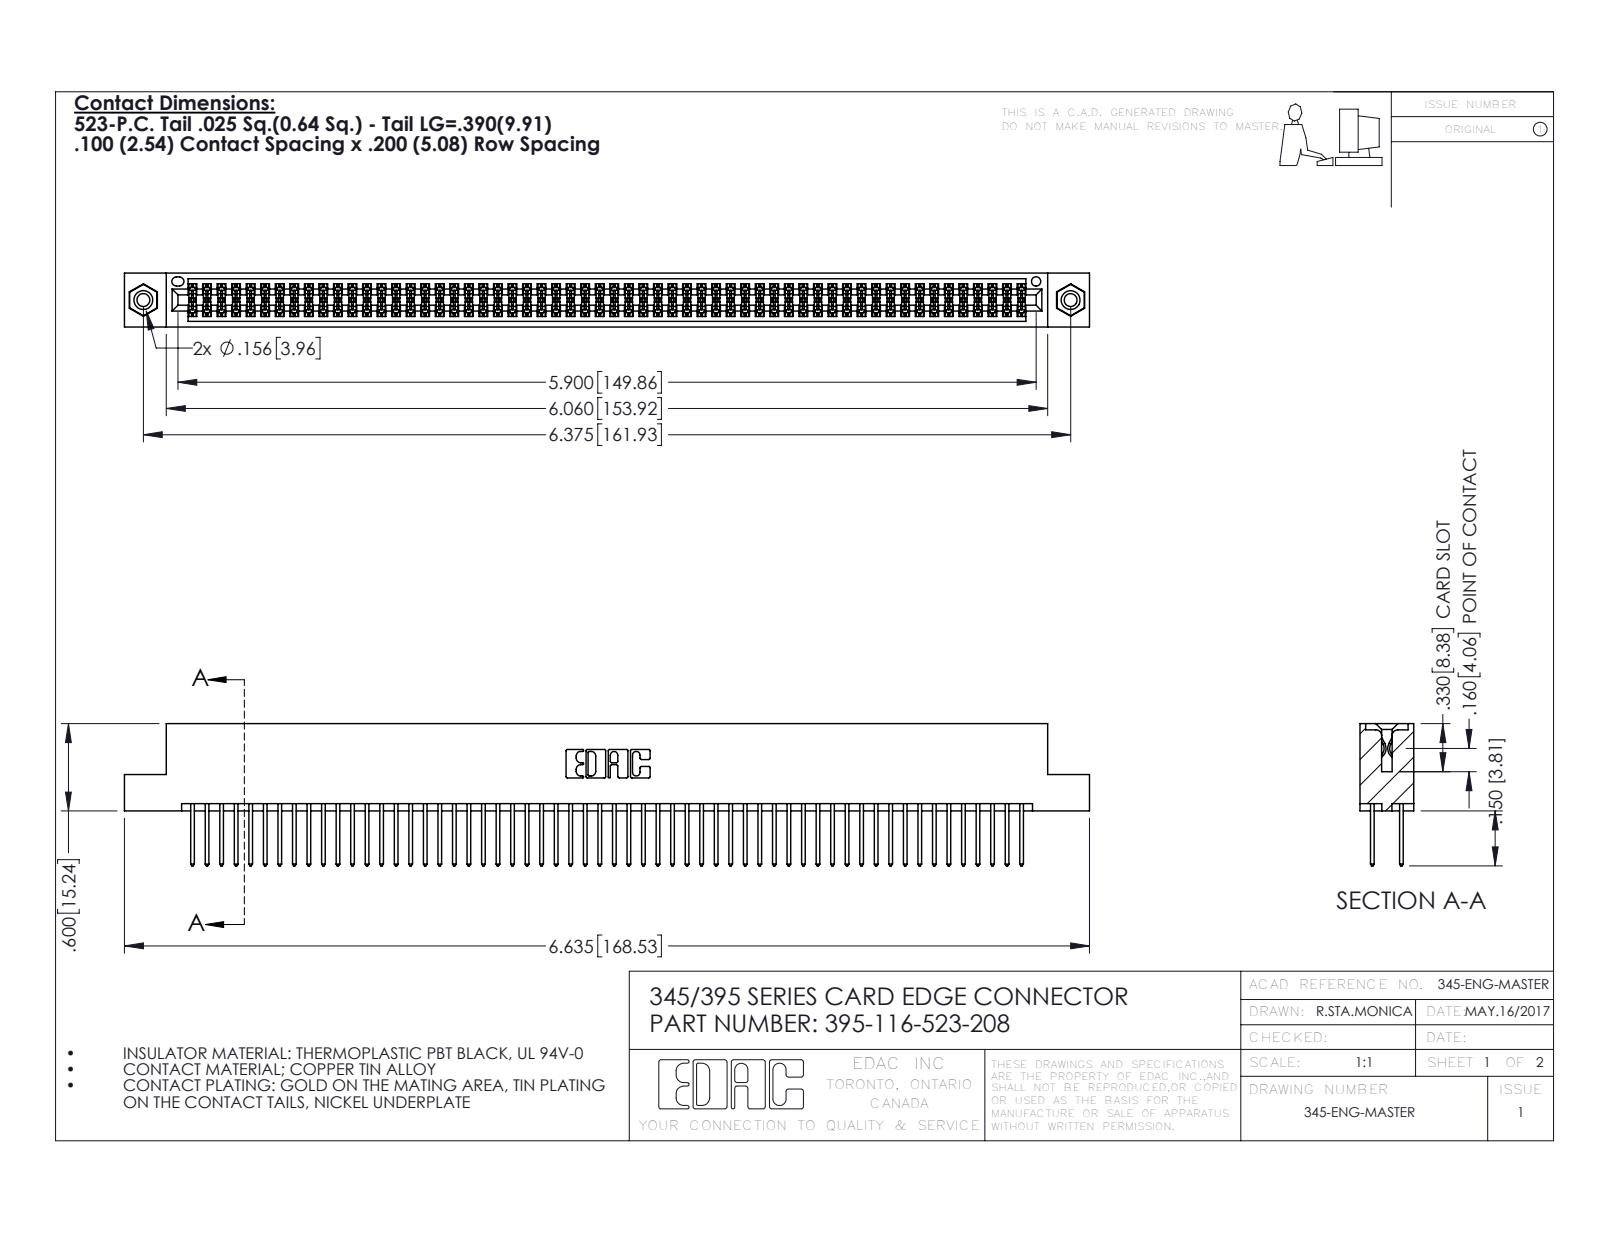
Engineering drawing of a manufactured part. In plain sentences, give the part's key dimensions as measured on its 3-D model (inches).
The part is named "345-292-001_345-293-123; 395-116-523-208; 345 Part_Flush Mounting Lugs - 0.156 Dia-TI; 345-250-001_345-250-003-102". Its 3-D file was written by "SolidWorks 2016 (CONFIG_CONTROL_DESIGN)". It is 119 solids with 5986 faces: 3940 planar, 2030 cylindrical and 16 other. Overall it measures 6.635 by 0.977 by 0.37 inches. Its volume is 1.022 cubic inches and its surface area 40.53 square inches. Round holes: 2 of diameter 0.089, 2 of diameter 0.125, 2 of diameter 0.156, 1 of diameter 0.064. Round bosses or shafts: 2 of diameter 0.155. Partial cylindrical surfaces (rounded edges, fillets, slot ends): 174 of radius 0.006, 116 of radius 0.01, 22 of radius 0.01, 6 of radius 0.007, 6 of radius 0.031, 3 of radius 0.026, 2 of radius 0.014, 2 of radius 0.019. The main face-to-face distances are 0.072, 0.298, 0.2, 0.098, 0.272, 0.025, 0.37, 0.225, 0.175, 0.149. The hole center spacings are 0.27, 6.139, 6.375.
